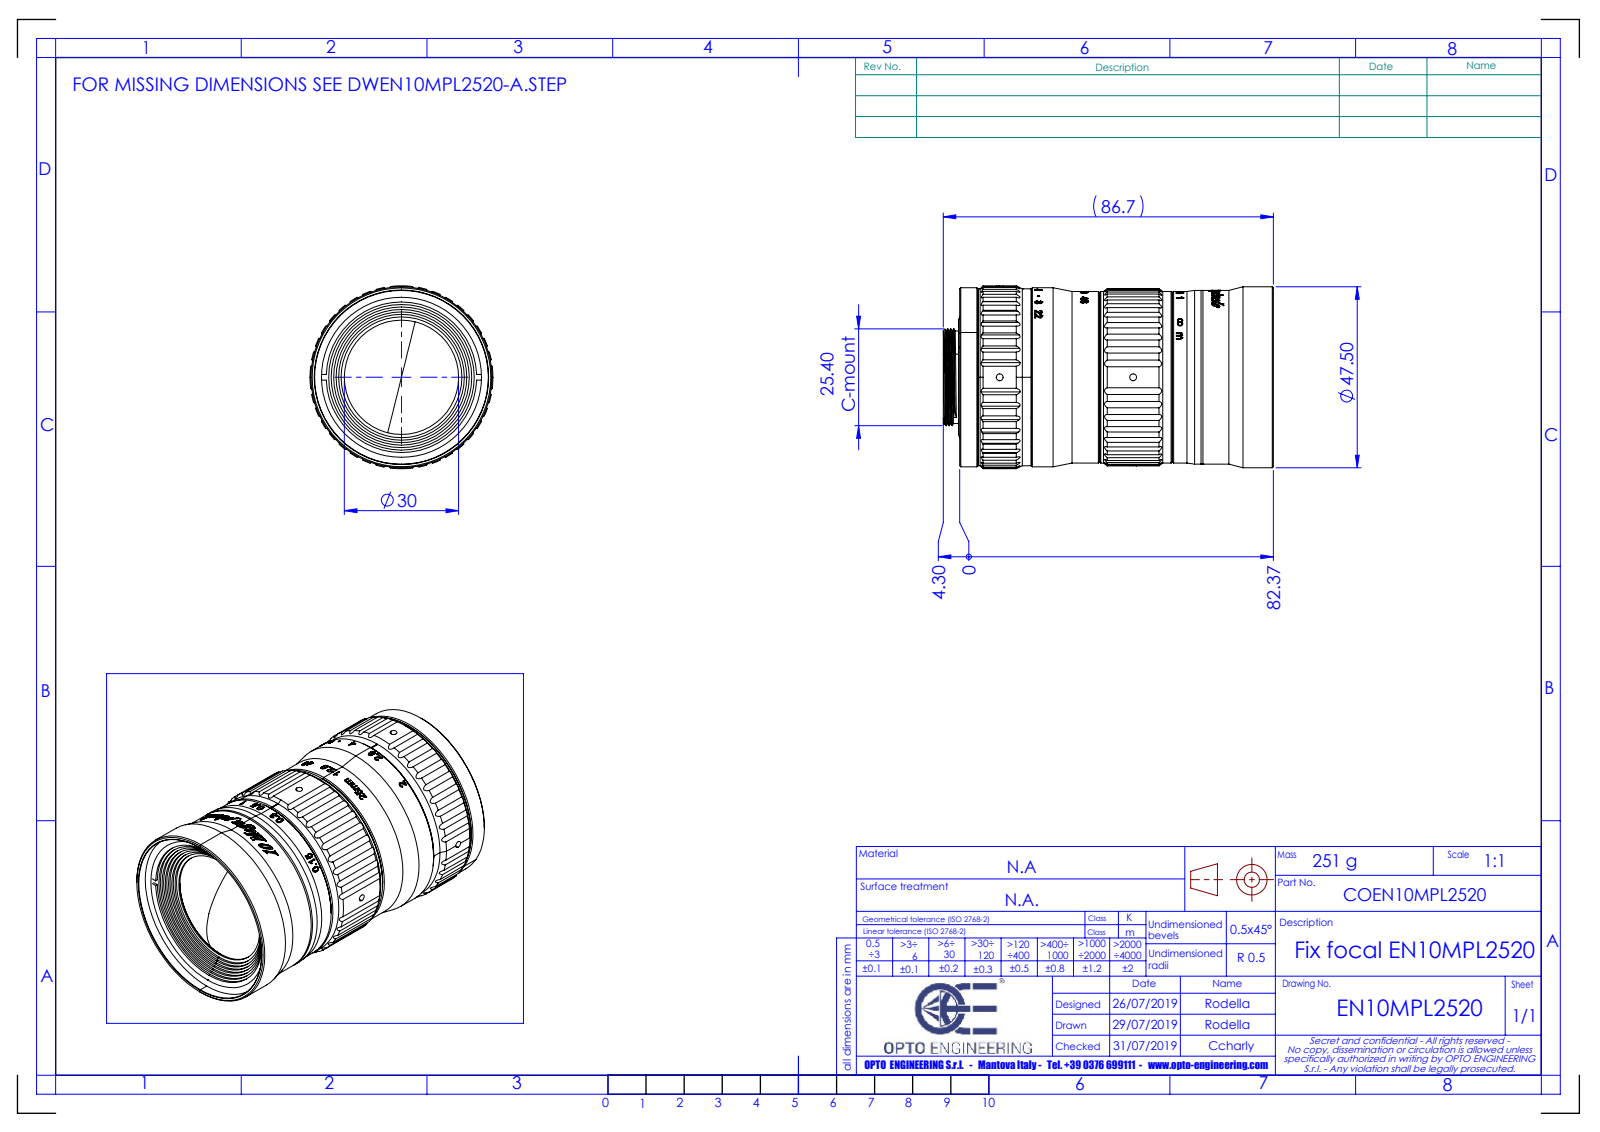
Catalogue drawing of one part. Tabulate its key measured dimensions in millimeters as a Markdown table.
| quantity | value |
| --- | --- |
| part name | 6690_ASM_ASM |
| STEP written by | PRO/ENGINEER BY PARAMETRIC TECHNOLOGY CORPORATION, 2011310 (AUTOMOTIVE_DESIGN) |
| units | millimeters |
| bodies | 2 solids, 1962 faces (470 planar, 591 cylindrical, 901 other) |
| overall size | 86.67 × 48 × 48 |
| volume | 42 947 mm³ |
| surface area | 68 784 mm² |
| round holes (diameter × count) | 1.5 × 13, 1.8 × 9, 2.6 × 5, 1 × 2, 2 × 2, 1.2 × 1, 1.7 × 1, 16 × 1, 17.4 × 1, 17.6 × 1, 19.4 × 1, 20.5 × 1 |
| round bosses / shafts (diameter × count) | 2.6 × 3, 1.8 × 3, 47.5 × 1, 47 × 1, 46.4 × 1, 45.6 × 1, 45 × 1, 43.6 × 1 |
| partial cylindrical surfaces (radius × count) | 1 × 74, 2 × 25, 1.25 × 7, 2.24 × 4, 5 × 3, 0.32 × 1, 0.32 × 1, 0.41 × 1 |
| main face-to-face distances | 2, 2.52, 68.19, 65.67, 74.71, 72.19, 6.52, 8.72, 6.2, 59.47 |
| hole center spacings | 19.5, 18.8, 32.49, 33.78, 18, 10.11, 24.12, 32.58 |
